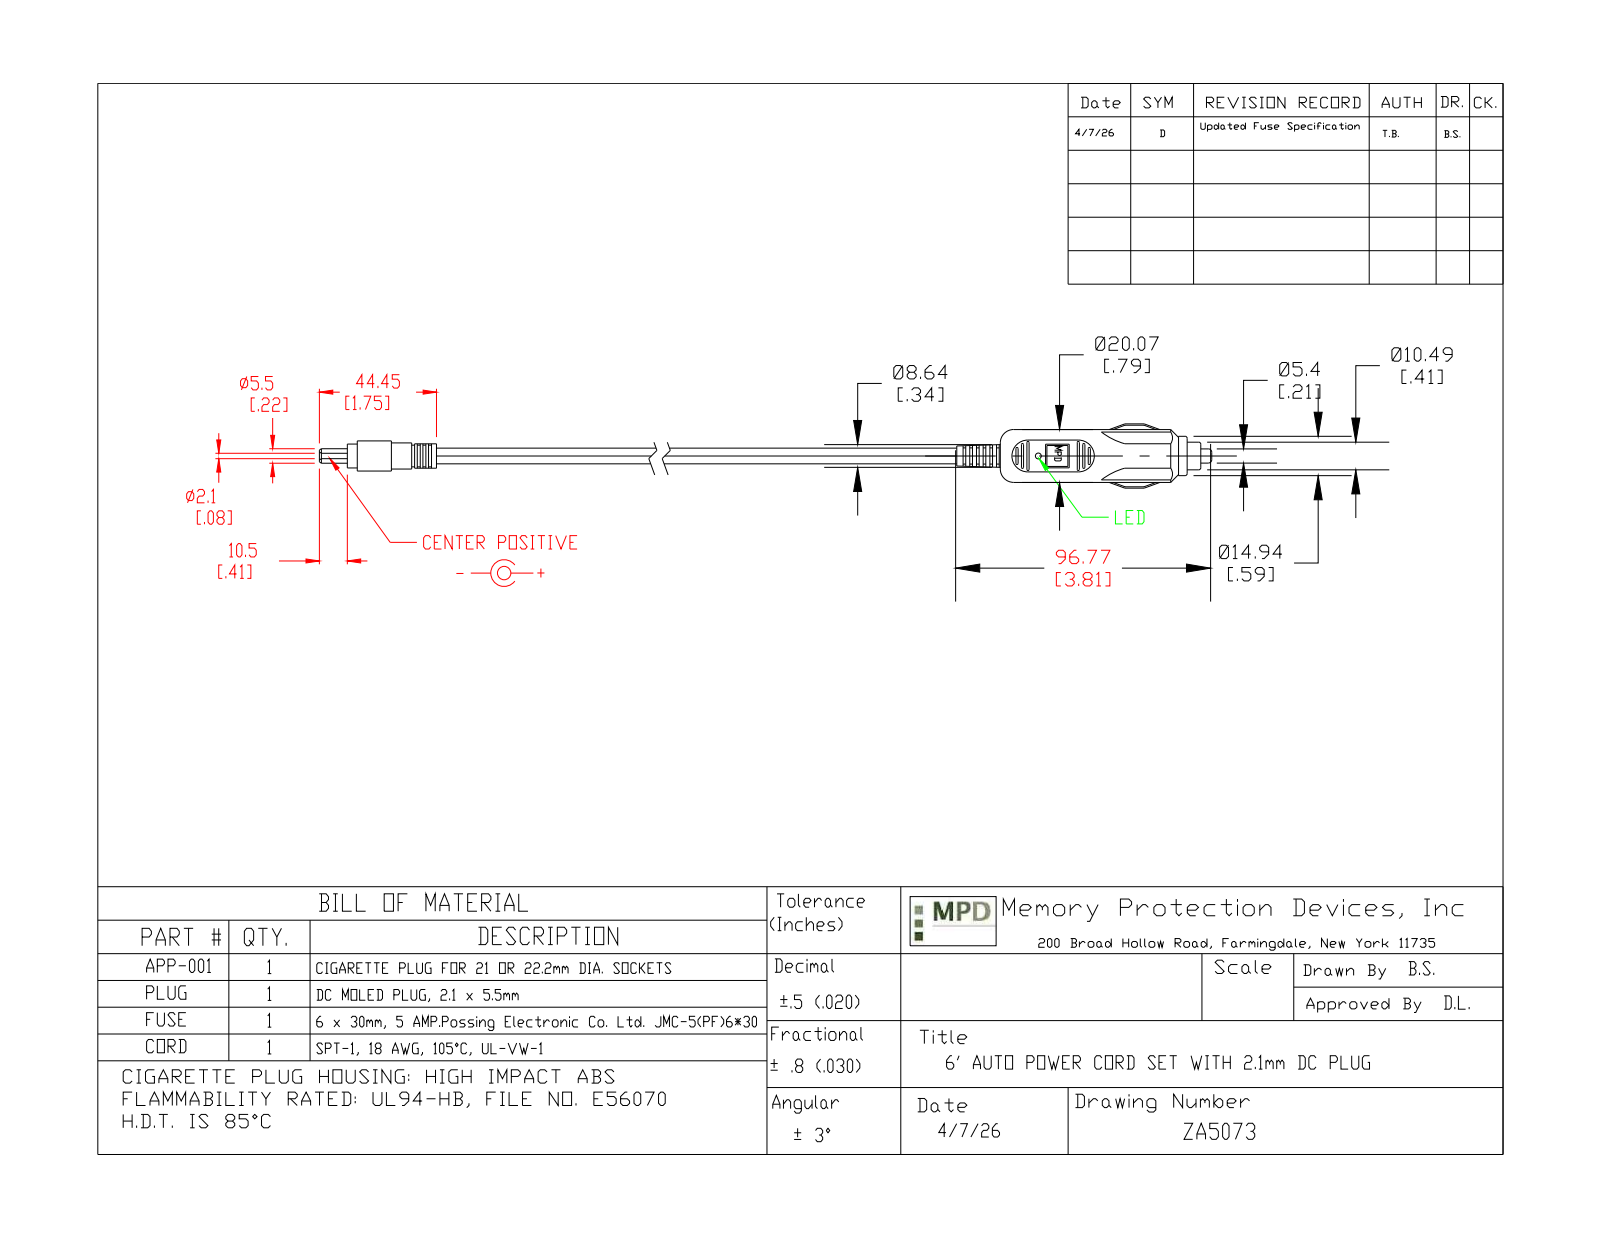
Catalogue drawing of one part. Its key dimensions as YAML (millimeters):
part_name: "dc plug-ZA5073; APP-001-ZA5073; ZA5073; cable-ZA5073"
step_written_by: "SolidWorks 2017 (AUTOMOTIVE_DESIGN)"
units: millimeters
bodies: {solids: 10, faces: 357, planar: 215, cylindrical: 66, other: 76}
overall_size: [178.42, 169.91, 20.07]
volume: 27876
surface_area: 15414
round_holes:
  - {diameter: 2.1, count: 1}
round_bosses_or_shafts:
  - {diameter: 2, count: 4}
  - {diameter: 20.07, count: 1}
  - {diameter: 14.94, count: 1}
  - {diameter: 11.42, count: 1}
  - {diameter: 10.49, count: 1}
  - {diameter: 8.99, count: 1}
  - {diameter: 5.5, count: 1}
  - {diameter: 5.4, count: 1}
partial_cylinders:
  - {radius: 0.2, count: 4}
  - {radius: 0.6, count: 4}
  - {radius: 6.5, count: 4}
  - {radius: 7.5, count: 4}
face_to_face_distances: [2.55, 16.08, 5.1, 0.4, 1.1, 1.45, 7.65, 3.65, 4, 19.07]
